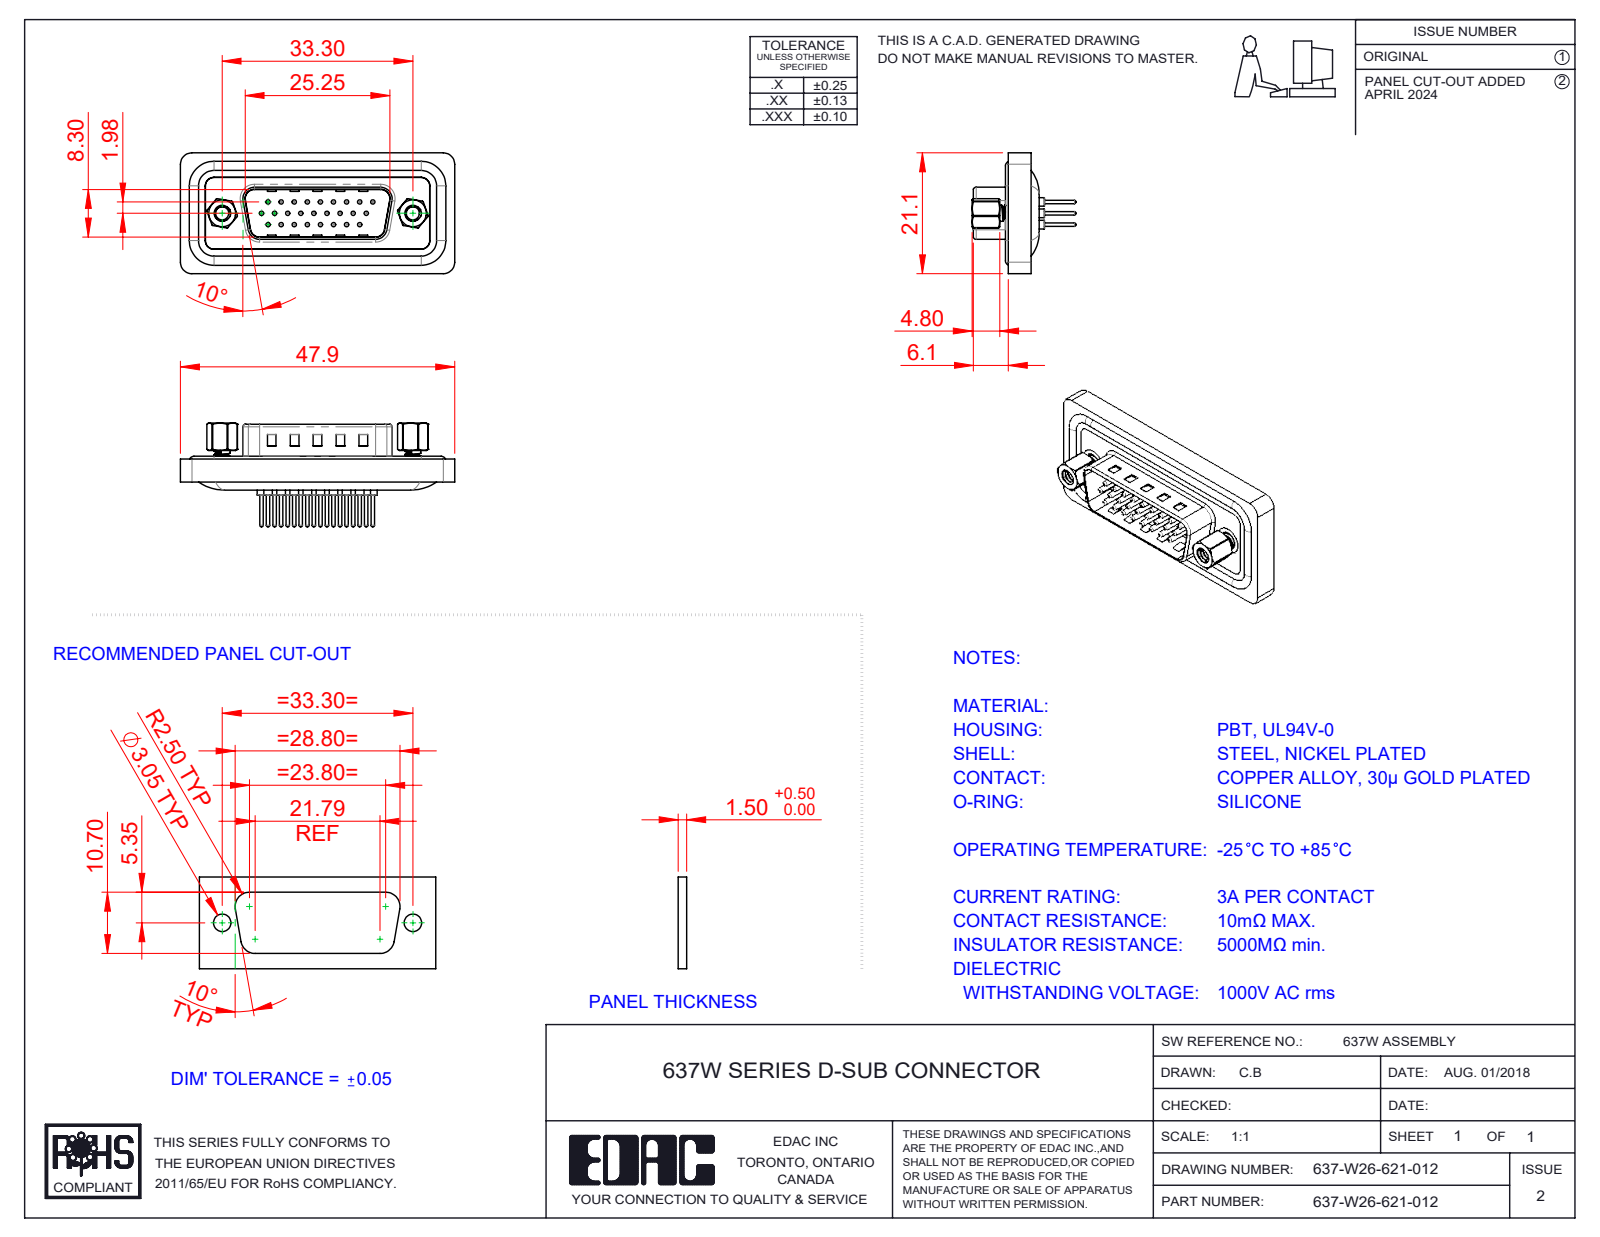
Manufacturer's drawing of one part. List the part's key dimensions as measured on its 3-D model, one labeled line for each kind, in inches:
Part name (STEP PRODUCT): 637W Contact Row 2_21; 637W Contact Row 1_21; 637-W26-621-012; 637W Shell_26 Contacts (+5 more)
STEP written by: SolidWorks 2016 (CONFIG_CONTROL_DESIGN)
Units: inches
Bodies: 34 solids, 1496 faces (355 planar, 628 cylindrical, 513 other)
Overall size (bounding box): 1.885 × 0.831 × 0.705
Volume: 0.299 in³ · Surface area: 13.63 in²
Round holes (diameter × count): ⌀0.03 ×26, ⌀0.059 ×26, ⌀0.063 ×26, ⌀0.079 ×26, ⌀0.089 ×2, ⌀0.09 ×2, ⌀0.157 ×2, ⌀0.189 ×2, ⌀0.197 ×2
Round bosses / shafts (diameter × count): ⌀0.059 ×26, ⌀0.024 ×26, ⌀0.063 ×4, ⌀0.193 ×2, ⌀0.11 ×2, ⌀0.197 ×1
Partial cylindrical surfaces — rounded edges, fillets, slot ends (radius × count): R0.079 ×16, R0.059 ×14, R0.02 ×8, R0.106 ×6, R0.035 ×4, R0.063 ×4, R0.169 ×4, R0.016 ×2
Main face-to-face distances: 0.016, 0.063, 0.043, 0.114, 0.098, 0.02, 0.222, 0.608, 0.03, 0.134
Hole centre spacings: 0.156, 0.09, 0.18, 0.238, 0.09, 0.324, 0.27, 0.238
